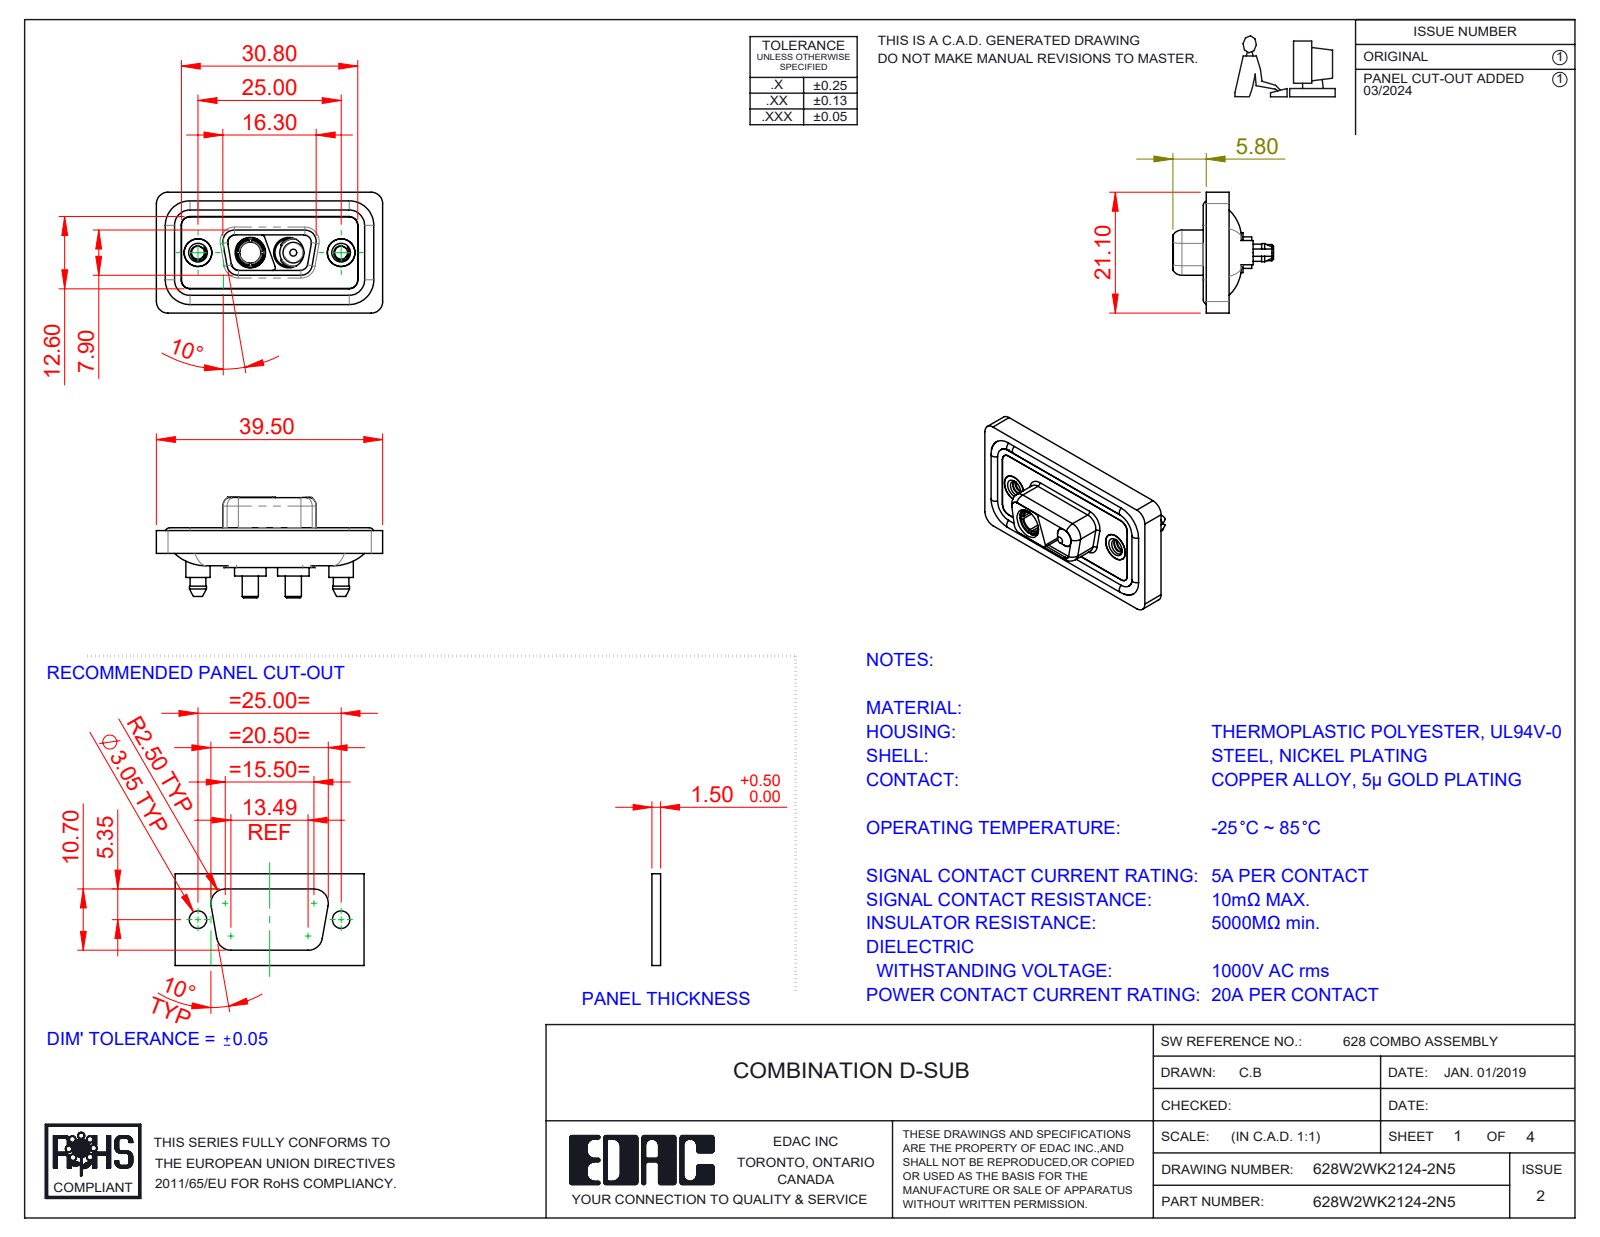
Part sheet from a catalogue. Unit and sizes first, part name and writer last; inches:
Units: inches
Overall size (bounding box): 1.555 × 0.831 × 0.691
Round holes (diameter × count): ⌀0.191 ×4, ⌀0.089 ×2, ⌀0.157 ×2, ⌀0.159 ×2, ⌀0.197 ×2, ⌀0.209 ×2, ⌀0.146 ×1
Round bosses / shafts (diameter × count): ⌀0.063 ×4, ⌀0.217 ×2, ⌀0.213 ×2, ⌀0.205 ×2, ⌀0.195 ×2, ⌀0.189 ×2, ⌀0.187 ×2, ⌀0.167 ×2
Partial cylindrical surfaces — rounded edges, fillets, slot ends (radius × count): R0.059 ×24, R0.079 ×18, R0.063 ×10, R0.053 ×8, R0.02 ×6, R0.01 ×4, R0.024 ×4, R0.026 ×4
Main face-to-face distances: 0.016, 0.043, 0.114, 0.063, 0.02, 0.071, 0.222, 0.059, 0.157, 0.211
Hole centre spacings: 0.36, 0.624, 0.265, 0.984
Volume: 0.289 in³ · Surface area: 11.9 in²
Bodies: 11 solids, 550 faces (160 planar, 263 cylindrical, 127 other)
Part name (STEP PRODUCT): 628Combo Threaded Boardlock_5; Power Socket_20A S; 628W2WK2124-2N5; 628Combo Shell Rear_09 Contacts (+4 more)
STEP written by: SolidWorks 2023 (CONFIG_CONTROL_DESIGN)
